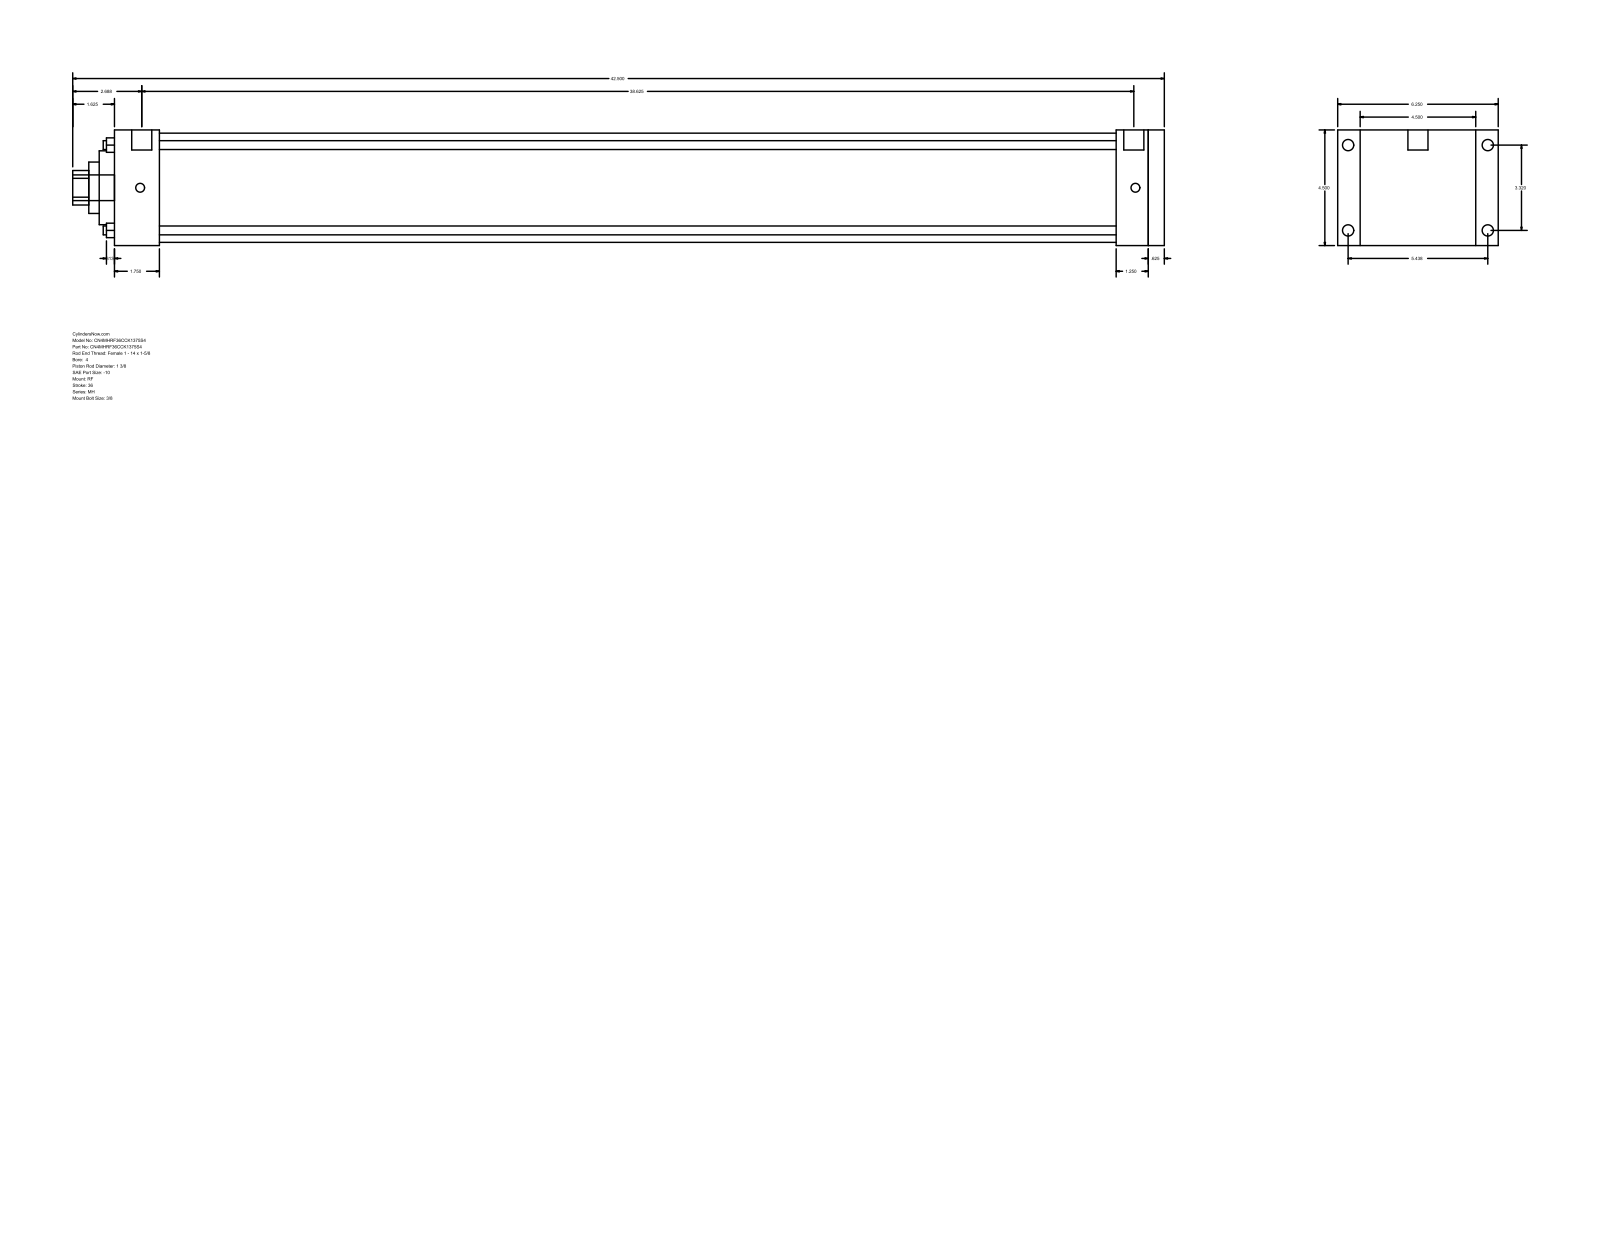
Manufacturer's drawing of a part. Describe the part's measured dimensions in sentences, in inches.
The part is named "MH_RF__0400_1.375". Its 3-D file was written by "GSSL Pune (CONFIG_CONTROL_DESIGN)". It is 0 solids with 94 faces: 65 planar, 29 cylindrical and 0 other. Overall it measures 42.5 by 6.25 by 4.5 inches. Round holes: 4 of diameter 0.345, 1 of diameter 1.375, 1 of diameter 2, 1 of diameter 2.875, 1 of diameter 4.25. Round bosses or shafts: 4 of diameter 0.438, 4 of diameter 0.344, 2 of diameter 0.781, 1 of diameter 1. Partial cylindrical surfaces (rounded edges, fillets, slot ends): 1 of radius 0.672. The main face-to-face distances are 4.5, 40.875, 0.625, 40.25, 1.75, 38.5, 39.125, 39, 37.25, 1.25. The hole center spacings are 2.347, 3.32, 4.695.
